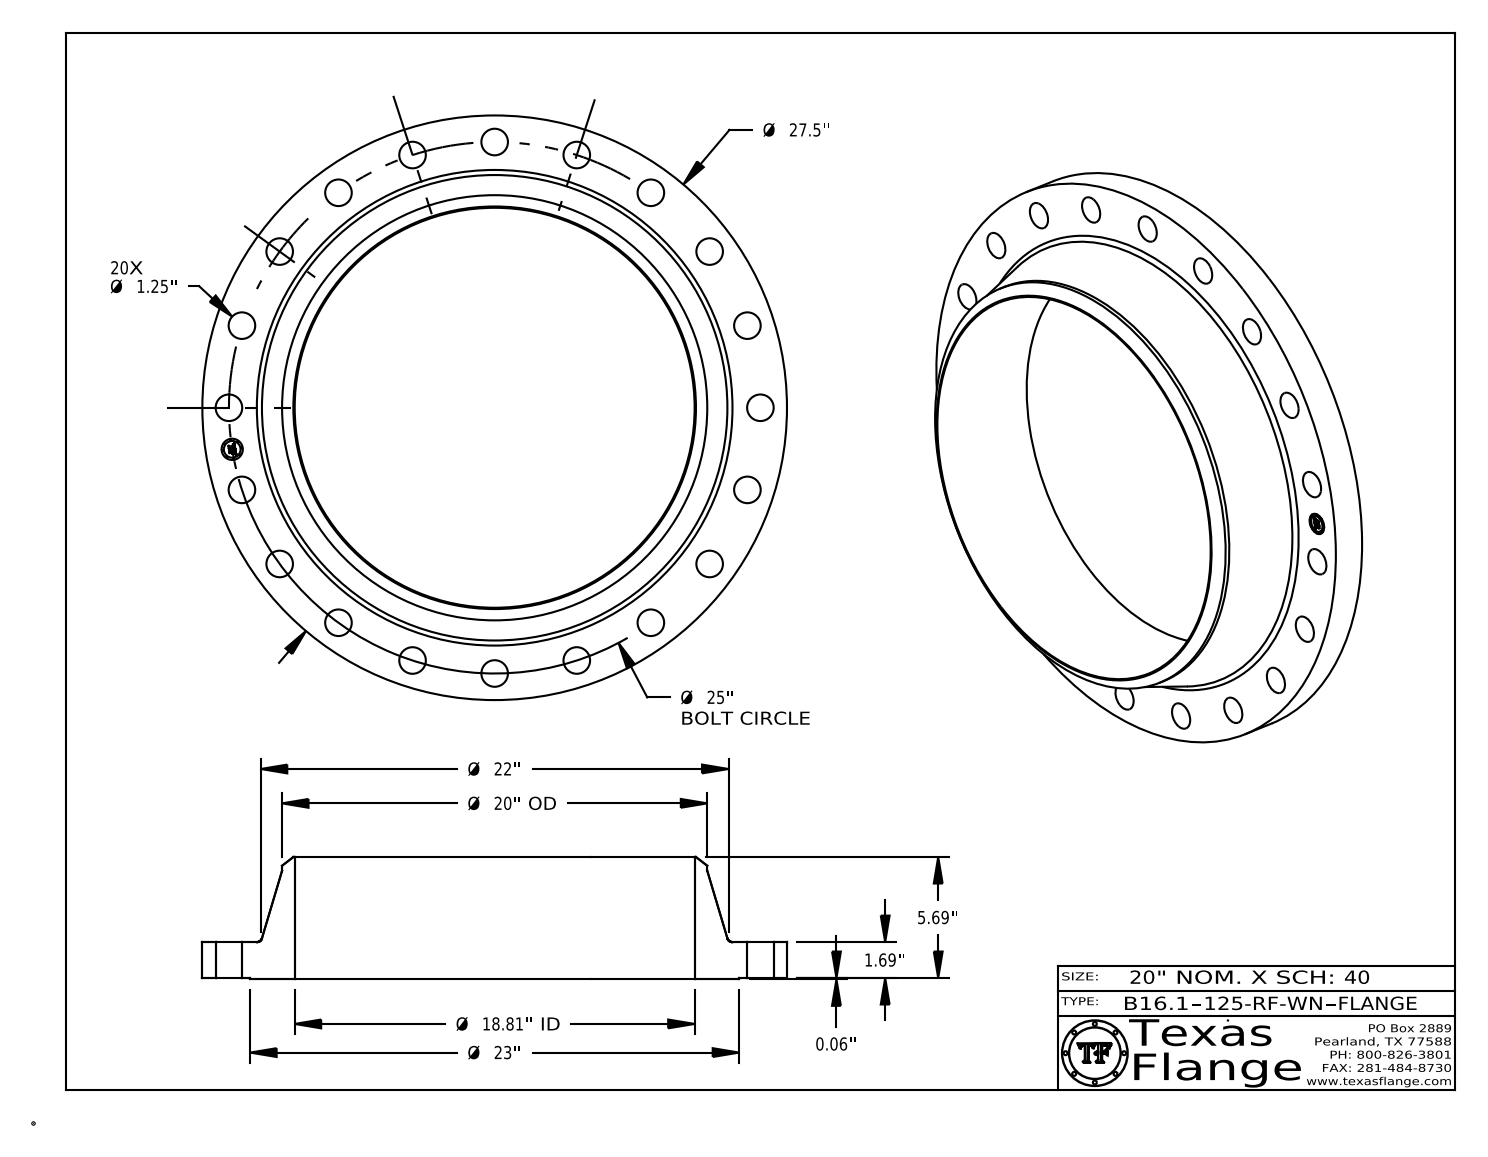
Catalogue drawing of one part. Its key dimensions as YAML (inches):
part_name: "B16.1, Class 125-RF-WN"
step_written_by: "CATIA V5 STEP AP214 (AUTOMOTIVE_DESIGN)"
units: inches
bodies: {solids: 1, faces: 443, planar: 369, cylindrical: 68, other: 6}
overall_size: [27.5, 27.5, 5.753]
volume: 748.8
surface_area: 1391
round_holes:
  - {diameter: 1.25, count: 20}
  - {diameter: 1, count: 1}
  - {diameter: 18.812, count: 1}
round_bosses_or_shafts:
  - {diameter: 0.061, count: 8}
  - {diameter: 27.5, count: 1}
  - {diameter: 23, count: 1}
  - {diameter: 20, count: 1}
  - {diameter: 0.788, count: 1}
face_to_face_distances: [1.69, 0.063, 1.753, 5.753, 5.69, 4, 1.738, 1.675, 0.015, 4.015]
hole_center_spacings: [12.5, 14.694, 17.678, 20.225, 23.776, 24.692, 11.35, 22.275]
